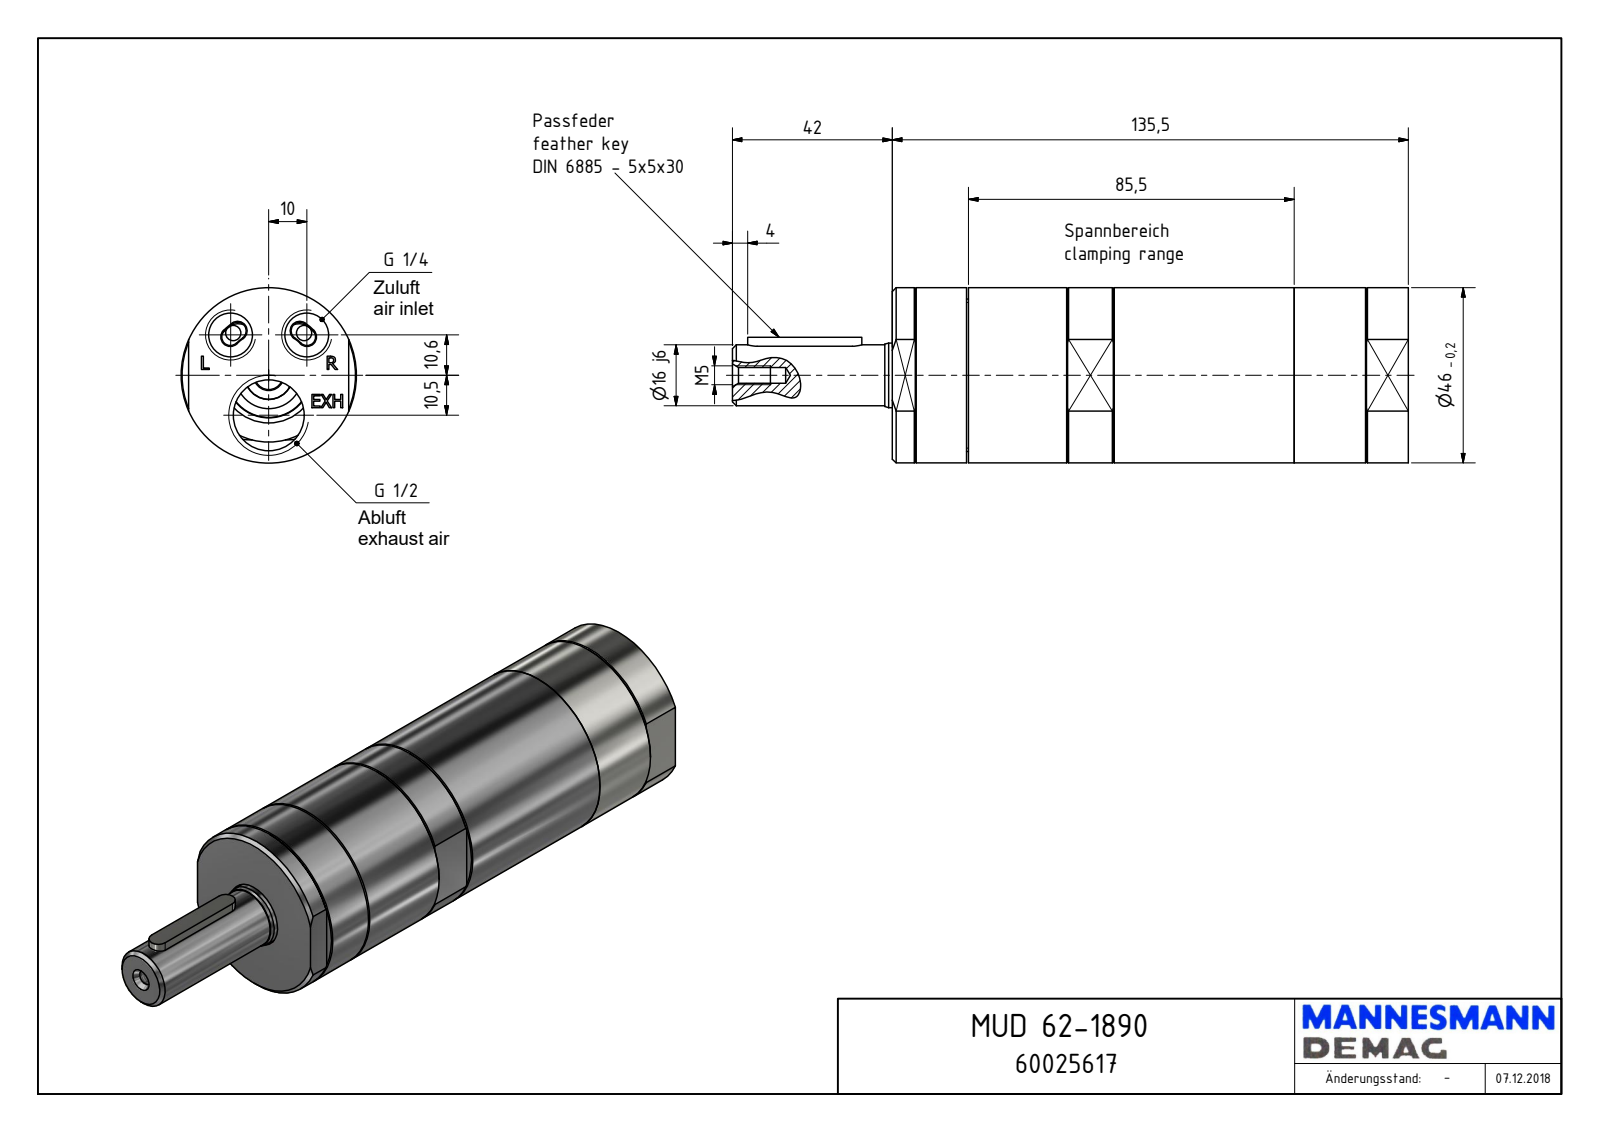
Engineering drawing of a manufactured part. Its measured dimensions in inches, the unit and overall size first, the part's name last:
Units: inches
Overall size (bounding box): 6.988 × 1.811 × 1.811
Round holes (diameter × count): ⌀0.451 ×2, ⌀0.163 ×1, ⌀0.689 ×1, ⌀0.733 ×1, ⌀0.846 ×1, ⌀0.906 ×1
Round bosses / shafts (diameter × count): ⌀1.811 ×1, ⌀1.575 ×1, ⌀1.31 ×1, ⌀0.77 ×1, ⌀0.667 ×1, ⌀0.63 ×1
Partial cylindrical surfaces — rounded edges, fillets, slot ends (radius × count): R0.098 ×6, R0.197 ×2, R0.659 ×1, R0.748 ×1
Main face-to-face distances: 5.335, 1.654, 0.787, 4.547, 0.768, 0.02, 4.567, 5.043, 4.275, 4.255
Hole centre spacings: 0.574, 0.919, 0.413, 0.787
Volume: 13.85 in³ · Surface area: 45.94 in²
Bodies: 1 solid, 171 faces (98 planar, 37 cylindrical, 36 other)
Part name (STEP PRODUCT): MUD 62-1890_60025617
STEP written by: Autodesk Inventor 2018 (AUTOMOTIVE_DESIGN)
